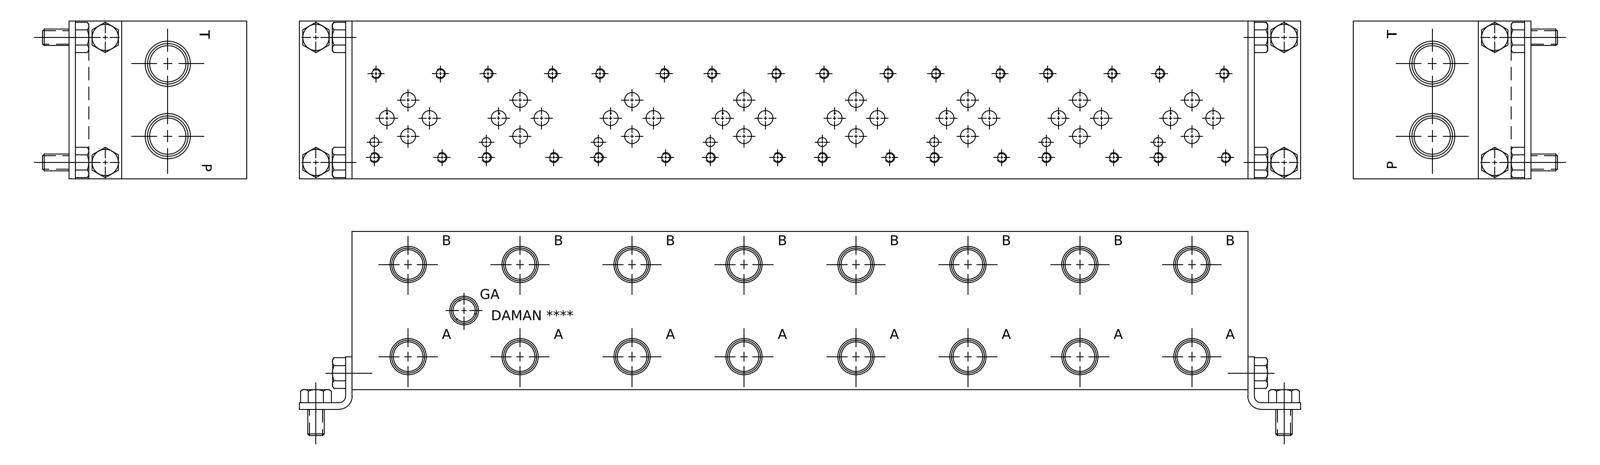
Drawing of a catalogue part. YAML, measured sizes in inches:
part_name: "Part_AD03P082P_3D"
step_written_by: "Autodesk Inventor 2020 (AUTOMOTIVE_DESIGN)"
units: inches
bodies: {solids: 1, faces: 1043, planar: 537, cylindrical: 158, other: 348}
overall_size: [17, 3, 3]
volume: 146.5
surface_area: 272.5
round_holes:
  - {diameter: 0.149, count: 32}
  - {diameter: 0.19, count: 32}
  - {diameter: 0.281, count: 24}
  - {diameter: 0.563, count: 16}
  - {diameter: 0.681, count: 16}
  - {diameter: 0.156, count: 8}
  - {diameter: 0.25, count: 8}
  - {diameter: 0.257, count: 2}
  - {diameter: 0.312, count: 2}
  - {diameter: 0.625, count: 2}
  - {diameter: 0.688, count: 2}
  - {diameter: 0.85, count: 2}
face_to_face_distances: [3, 17, 0.462, 2.538, 0.605, 16.395, 0.46, 2.998, 15.79, 2.37]
hole_center_spacings: [4.25, 8.5, 2.125, 2.125, 4.596, 6.375, 6.375, 12.75]
